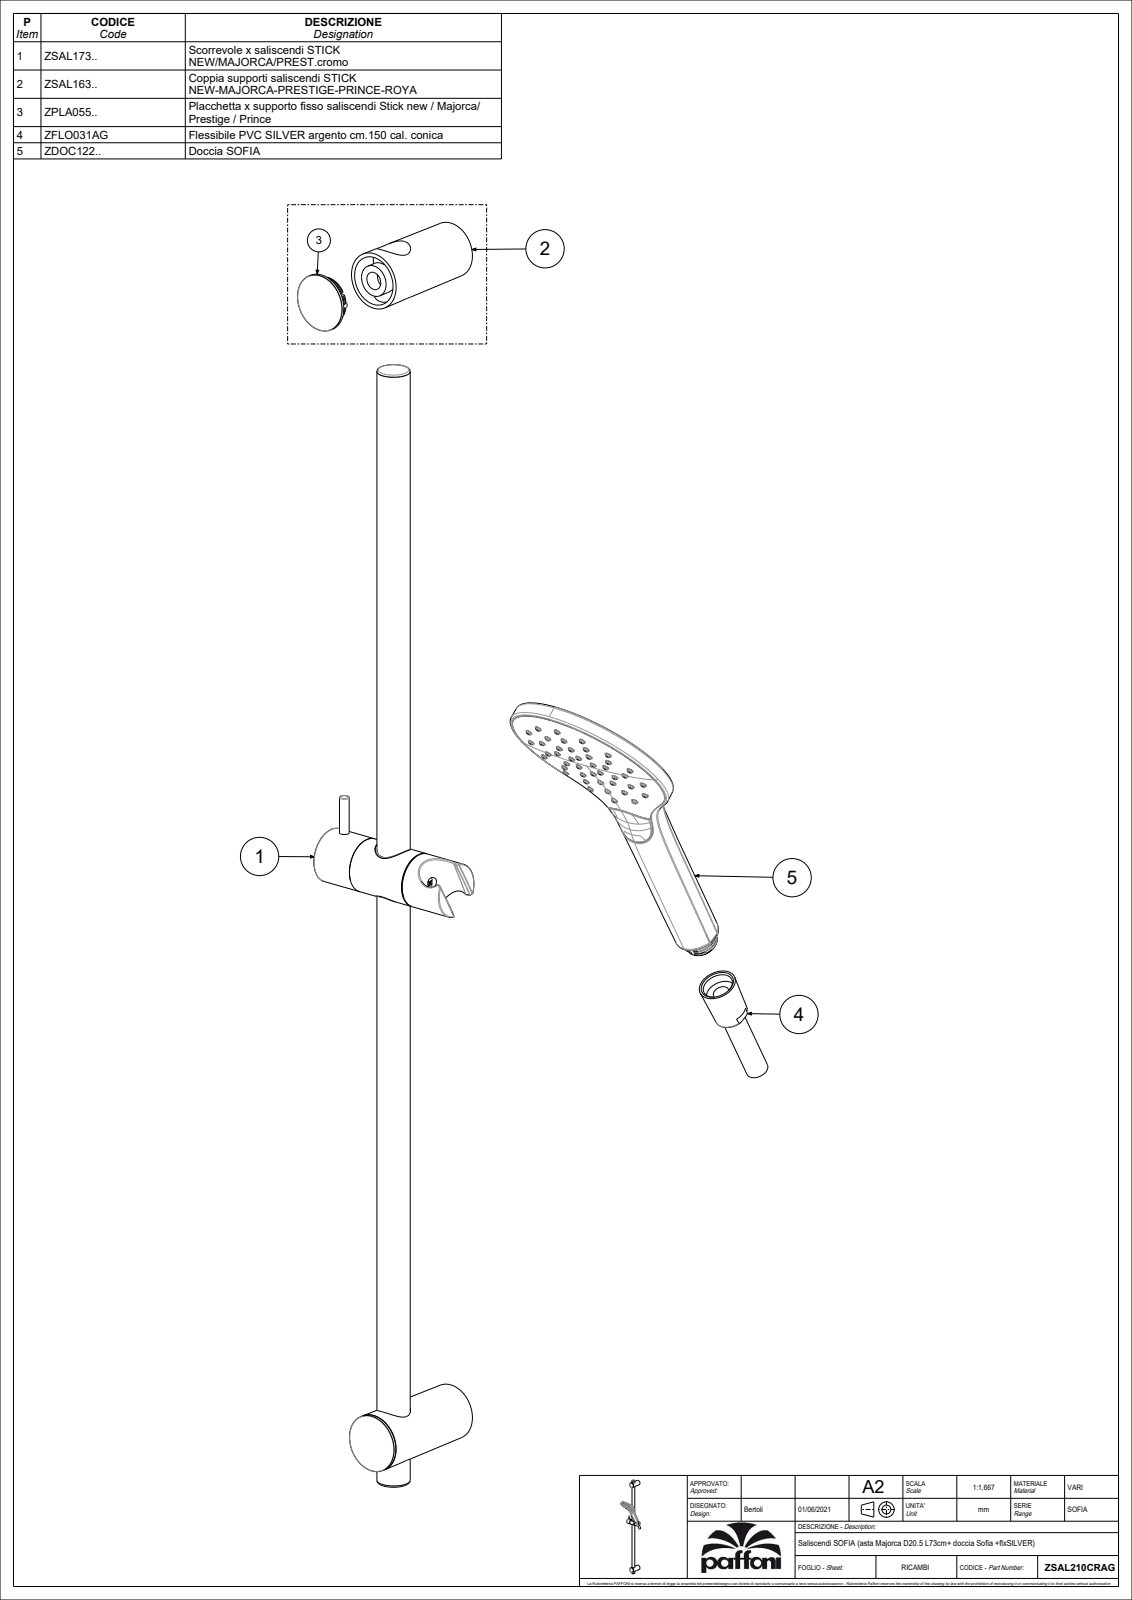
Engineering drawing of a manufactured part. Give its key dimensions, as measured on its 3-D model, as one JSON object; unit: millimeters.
{"part_name": "M50520-020_3; M50330-013_1; M50520-011_1; M50520-012_1 (+8 more)", "step_written_by": "CREO PARAMETRIC BY PTC INC, 2020044 (CONFIG_CONTROL_DESIGN)", "units": "millimeters", "bodies": {"solids": 35, "faces": 3913, "planar": 1049, "cylindrical": 832, "other": 2032}, "overall_size": [734, 147.09, 131.21], "volume_mm3": 190727, "surface_area_mm2": 301617, "round_holes": [[4, 5], [6, 4], [3, 3], [5.4, 2], [10, 2], [11, 2], [11.2, 2], [21, 2], [22.5, 2], [27, 2], [31, 2], [0.7, 1]], "round_bosses_or_shafts": [[7, 5], [31.2, 3], [12, 3], [36.5, 2], [35, 2], [25, 2], [22.4, 2], [20.5, 2]], "partial_cylinders_radius": [[0.2, 46], [0.5, 46], [0.3, 27], [1, 23], [1.5, 14], [19, 12], [0.6, 10], [18.5, 8]], "face_to_face_distances": [1.1, 366.51, 367.61, 365.41, 74, 3, 2.5, 2, 41.2, 36], "hole_center_spacings": [36, 15.93, 20.3, 24.86, 37.42, 38.65, 44.89, 48]}
